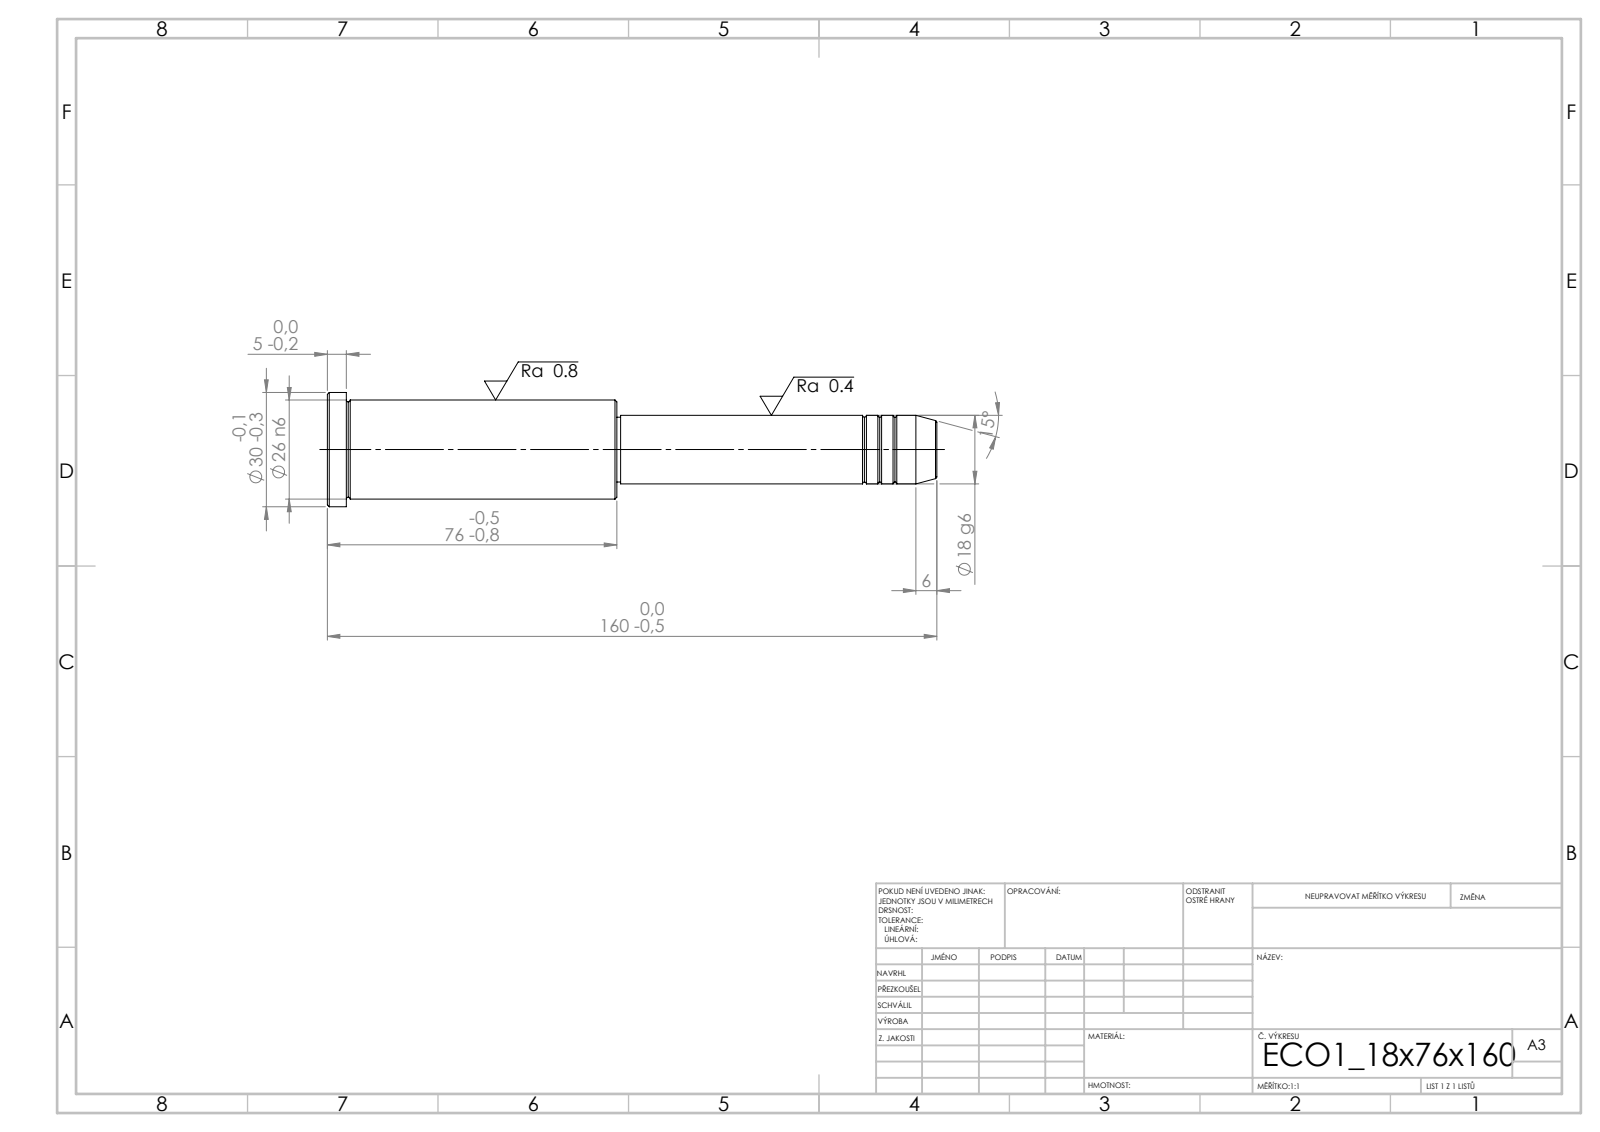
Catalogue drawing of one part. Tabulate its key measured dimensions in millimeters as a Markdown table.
| quantity | value |
| --- | --- |
| STEP written by | SolidWorks 2019 (CONFIG_CONTROL_DESIGN) |
| units | millimeters |
| bodies | 1 solid, 43 faces (5 planar, 14 cylindrical, 24 other) |
| overall size | 160 × 30 × 30 |
| volume | 62 242 mm³ |
| surface area | 12 468 mm² |
| round bosses / shafts (diameter × count) | 30 × 1, 26 × 1, 18 × 1, 17 × 1 |
| main face-to-face distances | 76, 71, 5, 84, 155, 160, 83, 1, 72, 77 |
